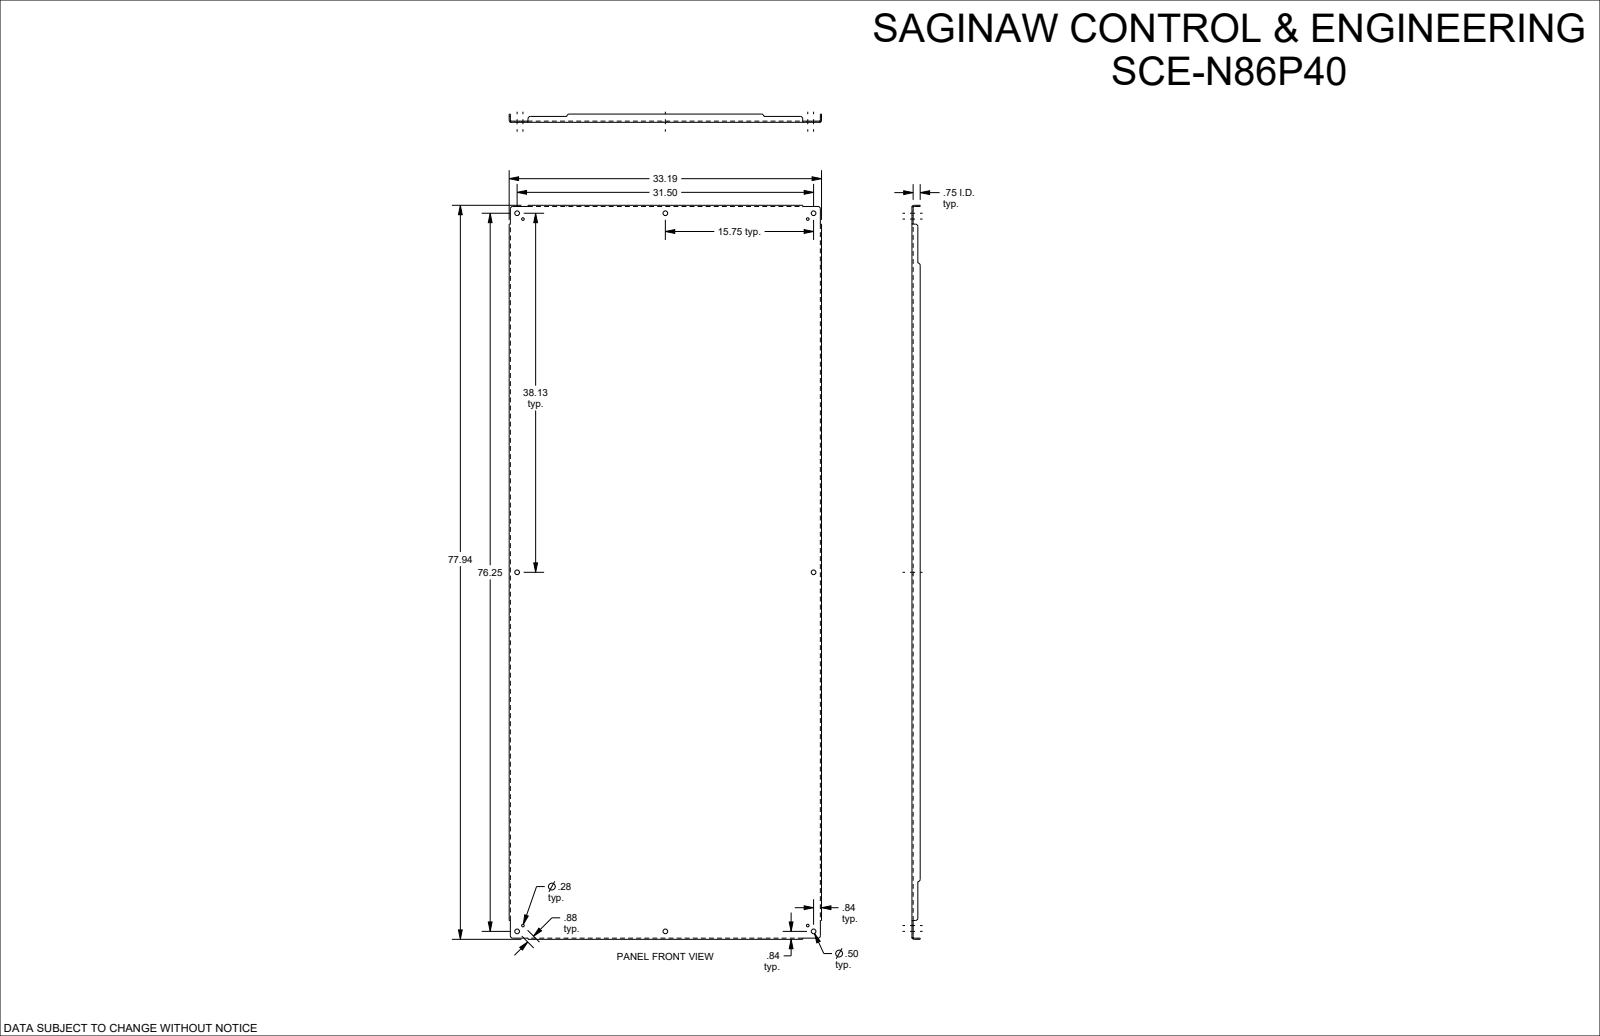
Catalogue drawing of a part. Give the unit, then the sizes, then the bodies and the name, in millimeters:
Units: millimetres
Overall size (bounding box): 1979.6 × 843 × 22.2
Round holes (diameter × count): ⌀12.7 ×8, ⌀7.1 ×4
Partial cylindrical surfaces — rounded edges, fillets, slot ends (radius × count): R6.4 ×12, R2.8 ×4, R6 ×4
Main face-to-face distances: 3.2, 839.8, 836.6, 842.9, 3.2, 1976.5, 19.1, 22.2, 1973.2, 1979.6
Hole centre spacings: 22.2, 384.7, 400.1, 784.5, 952.8, 968.4, 1047.8, 1234
Volume: 5 558 000 mm³ · Surface area: 3 521 000 mm²
Bodies: 1 solid, 122 faces (46 planar, 52 cylindrical, 24 other)
Part name (STEP PRODUCT): SCE-N86P40
STEP written by: SolidWorks 2023 (AUTOMOTIVE_DESIGN)
